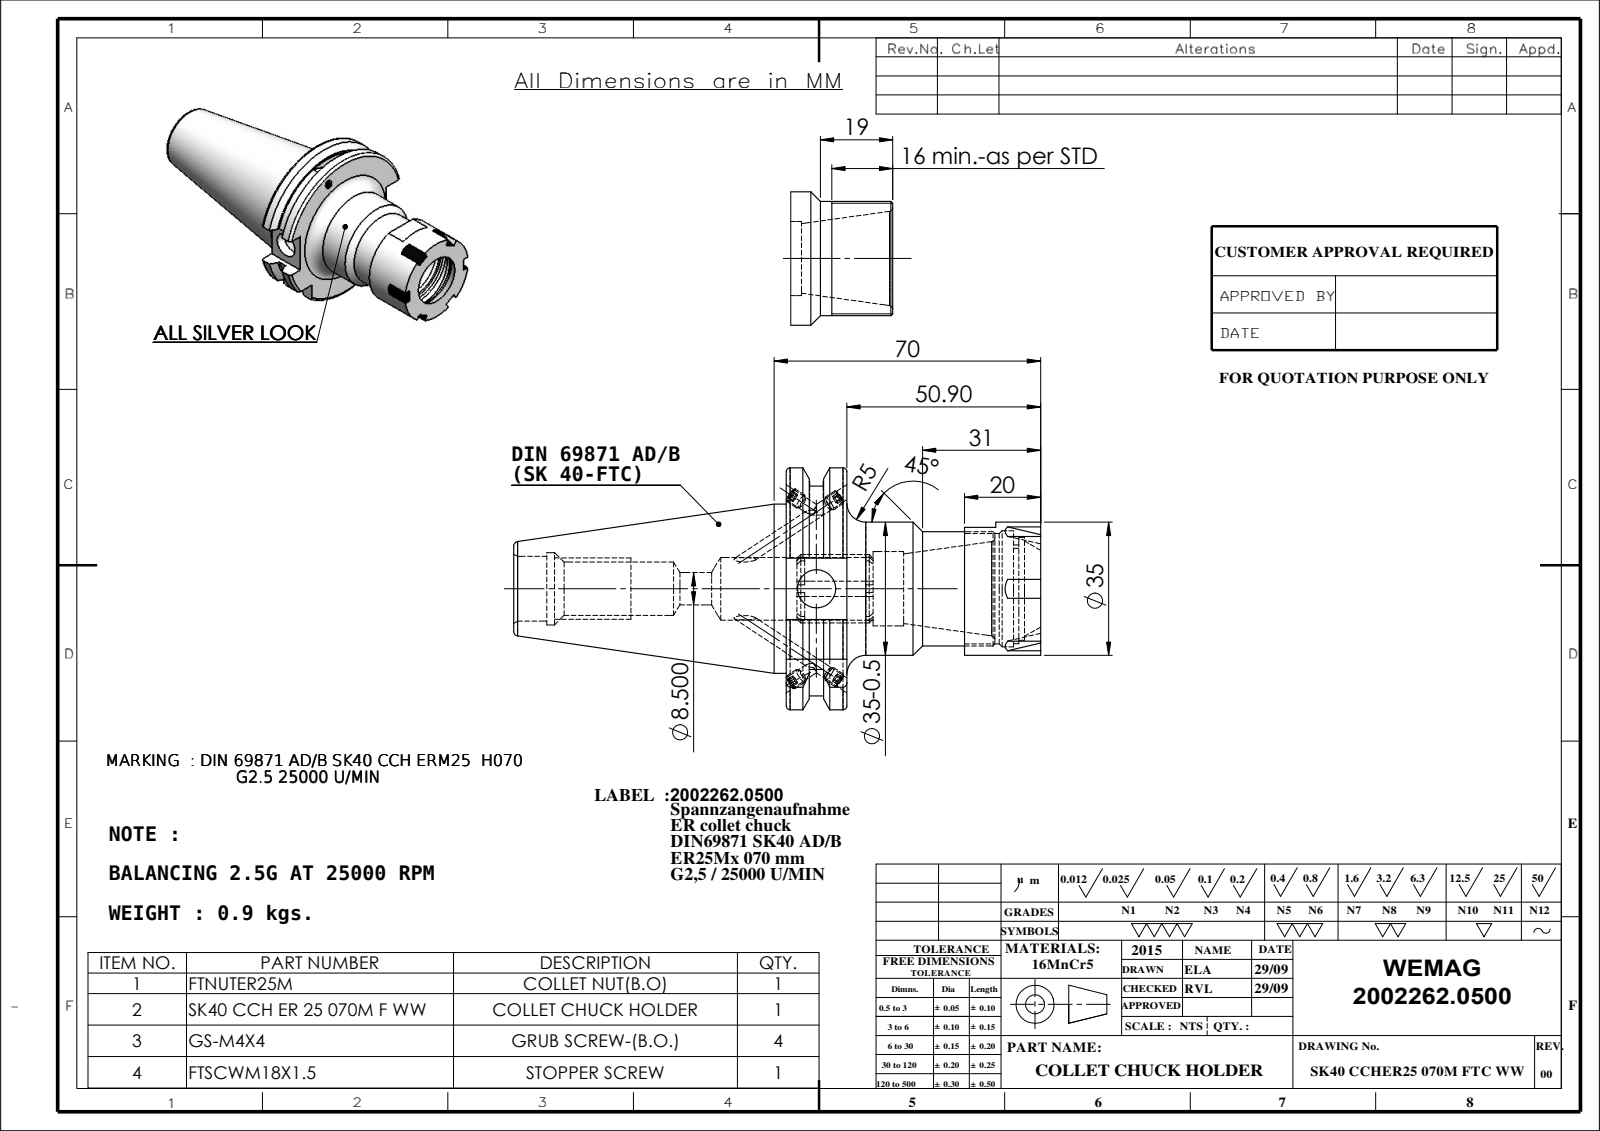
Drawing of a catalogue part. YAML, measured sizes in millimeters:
part_name: "SK40 CCH ER 25 070M F WW; FTNUTER25M; 91406-ERM725070; FTSCWM18X150 (+1 more)"
step_written_by: "SolidWorks 2009 (CONFIG_CONTROL_DESIGN)"
units: millimeters
bodies: {solids: 7, faces: 234, planar: 102, cylindrical: 64, other: 68}
overall_size: [138.4, 63.55, 61.48]
volume: 128627
surface_area: 35030
round_holes:
  - {diameter: 3.3, count: 4}
  - {diameter: 4, count: 1}
  - {diameter: 8.5, count: 1}
  - {diameter: 10, count: 1}
  - {diameter: 14, count: 1}
  - {diameter: 16.5, count: 1}
  - {diameter: 17, count: 1}
  - {diameter: 19, count: 1}
  - {diameter: 19.5, count: 1}
  - {diameter: 25.8, count: 1}
  - {diameter: 27, count: 1}
  - {diameter: 29, count: 1}
round_bosses_or_shafts:
  - {diameter: 4, count: 4}
  - {diameter: 44.45, count: 1}
  - {diameter: 35, count: 1}
  - {diameter: 30, count: 1}
  - {diameter: 18, count: 1}
partial_cylinders:
  - {radius: 11.5, count: 1}
  - {radius: 28.12, count: 1}
  - {radius: 31.77, count: 1}
face_to_face_distances: [15.9, 66.8, 50.9, 20, 44, 46.8, 30.9, 24, 22.8, 6.9]
hole_center_spacings: [35.11, 1.5]
